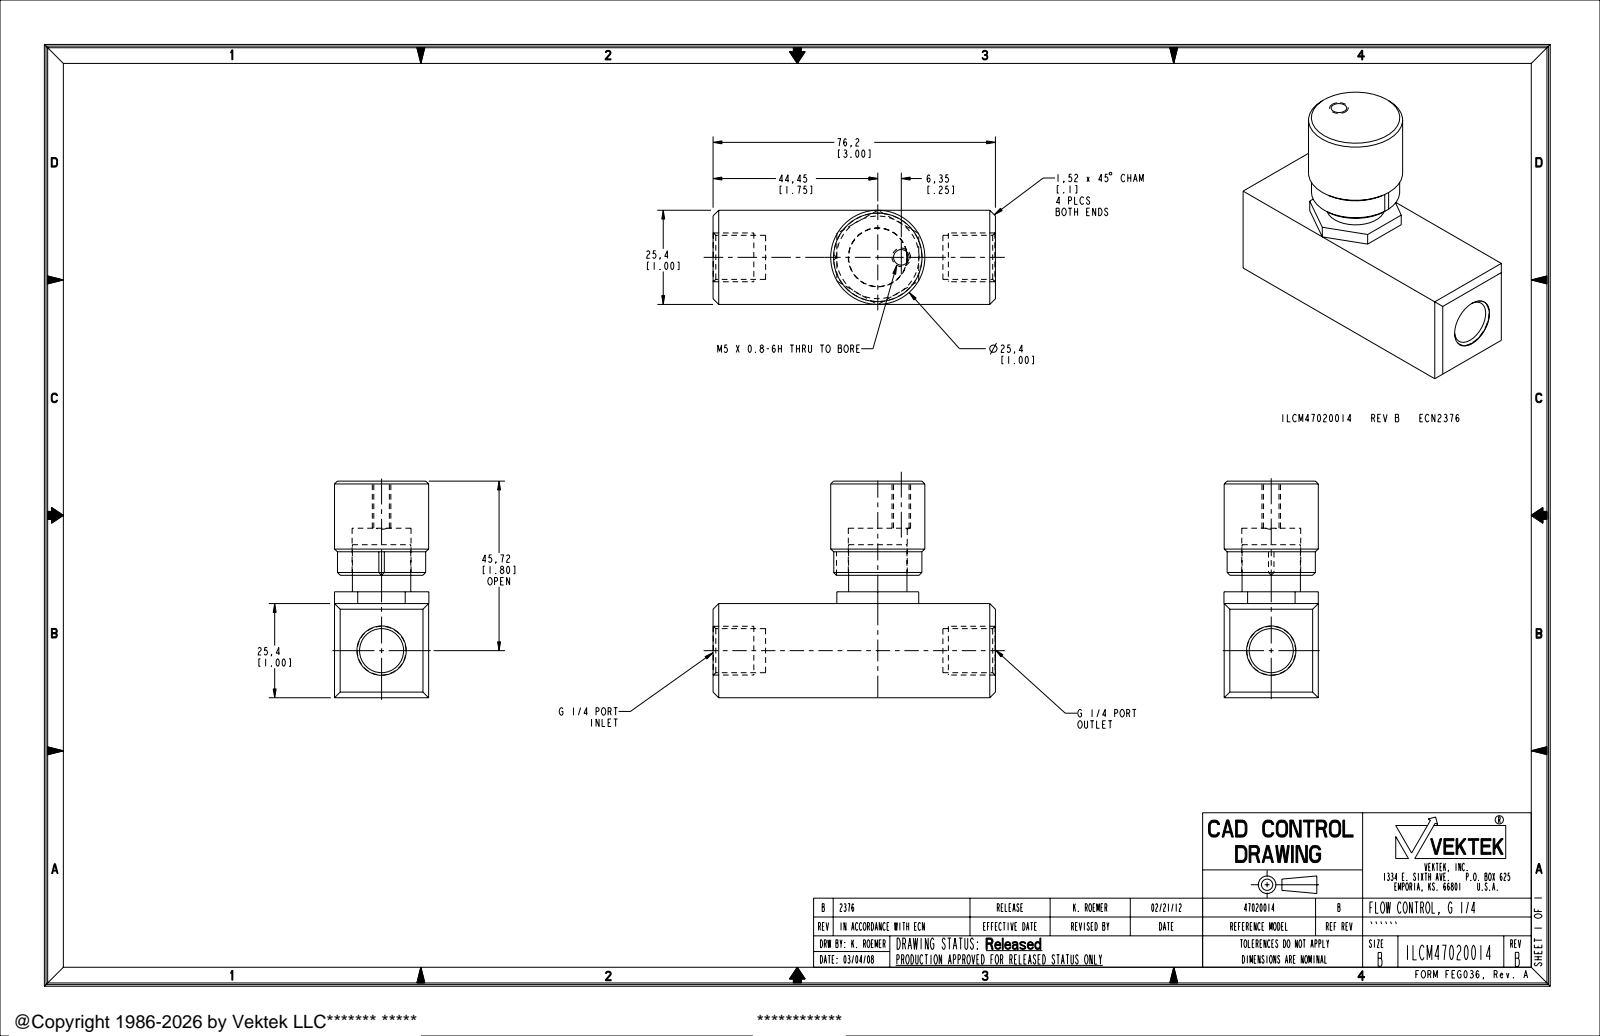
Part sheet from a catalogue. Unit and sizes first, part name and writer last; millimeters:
Units: millimetres
Overall size (bounding box): 76.2 × 58.42 × 25.46
Round holes (diameter × count): ⌀4.2 ×1, ⌀5 ×1, ⌀11.89 ×1, ⌀13.31 ×1, ⌀15.9 ×1
Round bosses / shafts (diameter × count): ⌀25.4 ×1, ⌀23.8 ×1, ⌀15.75 ×1, ⌀13.16 ×1
Main face-to-face distances: 25.4, 33.02, 58.42, 12.7, 76.2, 28.58, 3.18, 29.84, 14.17, 62.03
Hole centre spacings: 6.35
Volume: 59 294 mm³ · Surface area: 15 647 mm²
Bodies: 2 solids, 69 faces (35 planar, 23 cylindrical, 11 other)
Part name (STEP PRODUCT): ILCM47020014
STEP written by: PRO/ENGINEER BY PARAMETRIC TECHNOLOGY CORPORATION, 2007460 (AUTOMOTIVE_DESIGN_CC2)
